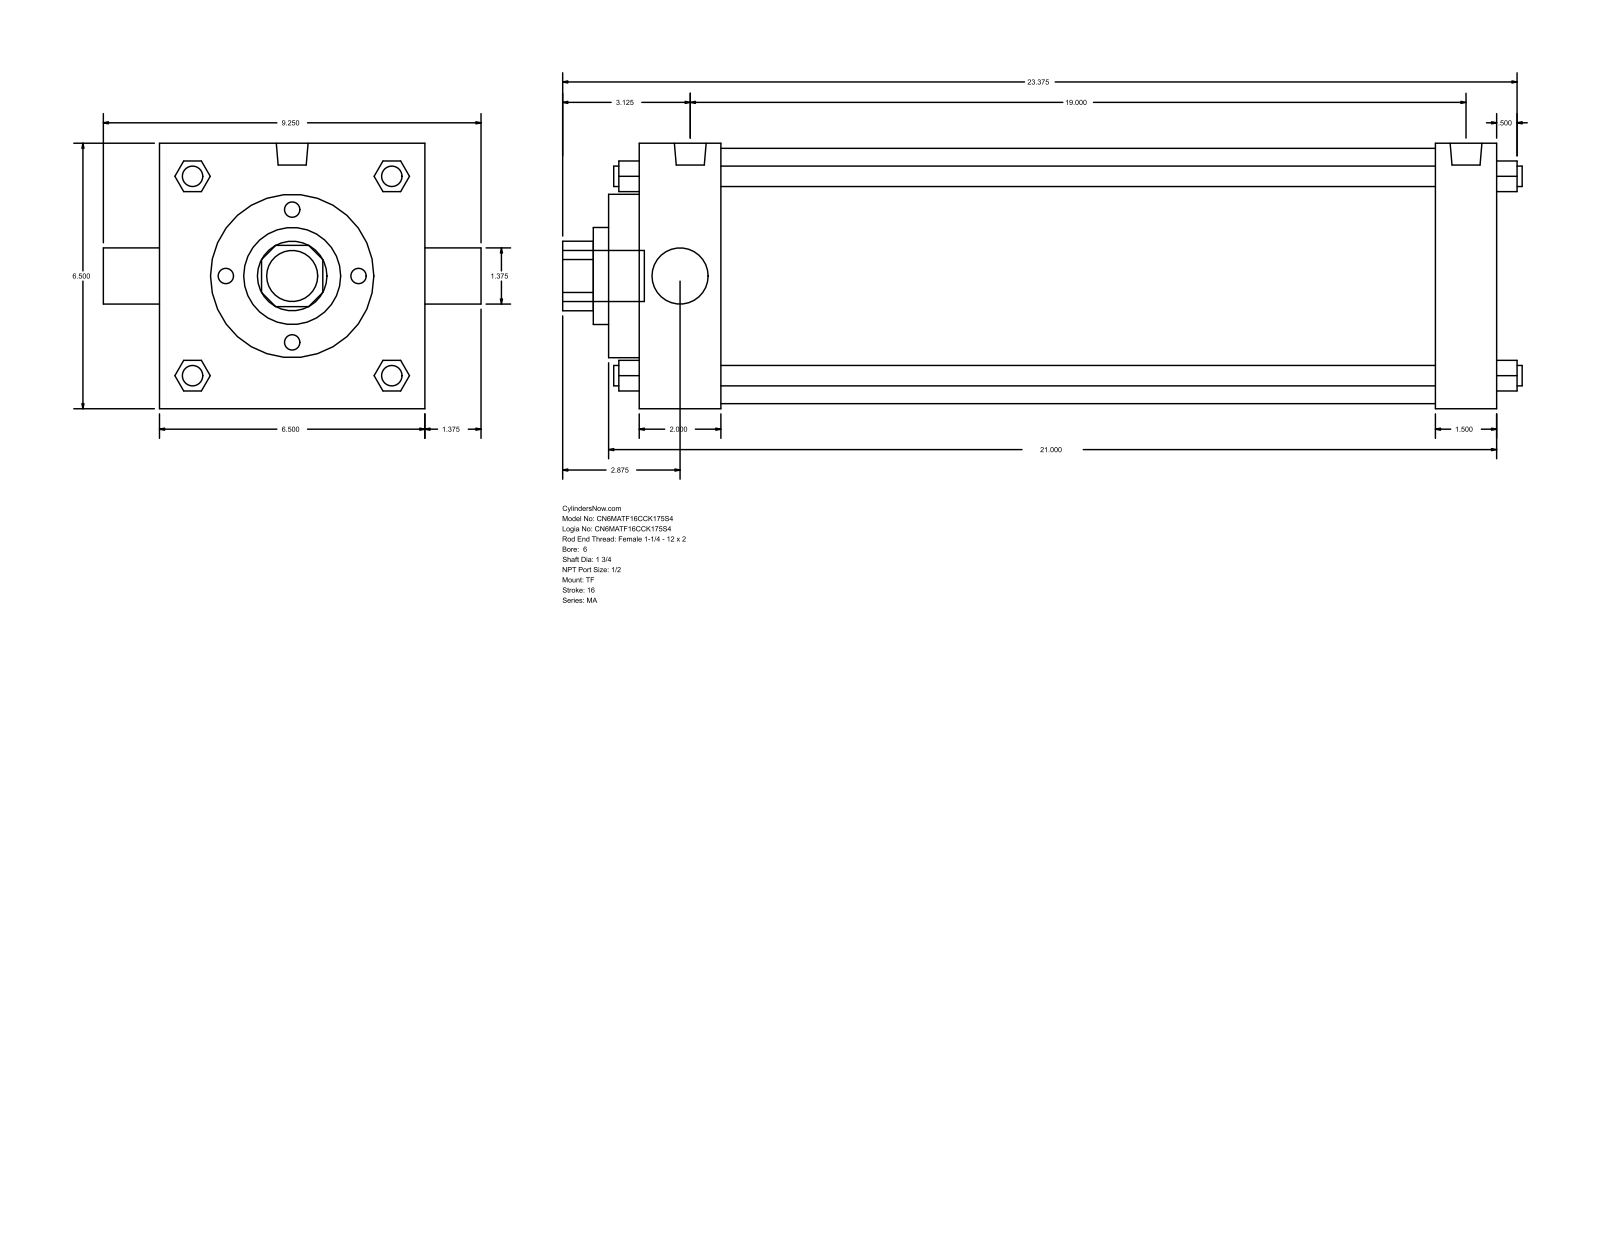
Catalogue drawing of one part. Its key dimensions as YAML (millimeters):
part_name: "MA_TF__0600_1.75"
step_written_by: "GSSL Pune (CONFIG_CONTROL_DESIGN)"
units: millimeters
bodies: {solids: 0, faces: 122, planar: 93, cylindrical: 29, other: 0}
overall_size: [596.9, 234.95, 165.1]
round_holes:
  - {diameter: 34.92, count: 1}
  - {diameter: 44.45, count: 1}
  - {diameter: 60.33, count: 1}
  - {diameter: 101.6, count: 1}
  - {diameter: 158.75, count: 1}
round_bosses_or_shafts:
  - {diameter: 12.7, count: 4}
  - {diameter: 17.46, count: 3}
  - {diameter: 19.77, count: 2}
  - {diameter: 31.75, count: 1}
partial_cylinders:
  - {radius: 21.63, count: 1}
face_to_face_distances: [165.1, 533.4, 19.05, 38.1, 50.8, 482.6, 495.3, 444.5, 69.85, 514.35]
